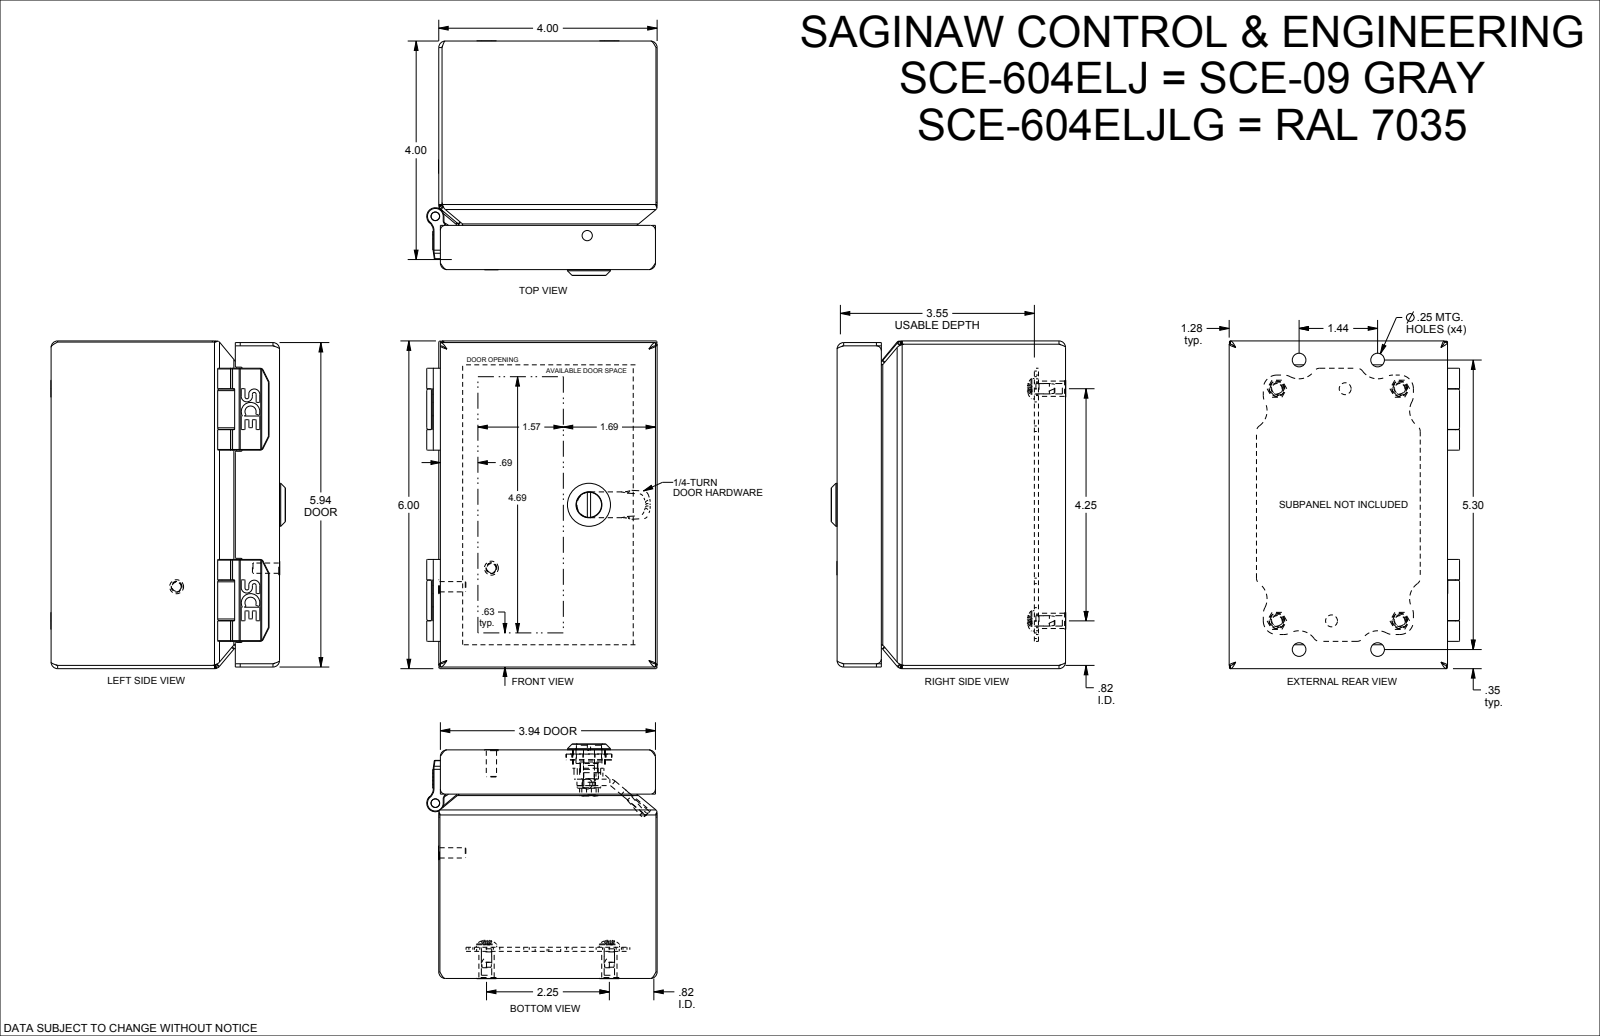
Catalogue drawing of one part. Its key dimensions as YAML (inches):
part_name: "SCE-604ELJLG"
step_written_by: "SolidWorks 2019 (CONFIG_CONTROL_DESIGN)"
units: inches
bodies: {solids: 0, faces: 2654, planar: 858, cylindrical: 764, other: 1032}
overall_size: [6, 4.296, 4.22]
round_holes:
  - {diameter: 0.25, count: 8}
  - {diameter: 0.19, count: 4}
  - {diameter: 0.284, count: 4}
  - {diameter: 0.479, count: 4}
  - {diameter: 0.02, count: 2}
  - {diameter: 0.1, count: 2}
  - {diameter: 0.174, count: 2}
  - {diameter: 0.196, count: 2}
  - {diameter: 0.218, count: 2}
  - {diameter: 0.266, count: 2}
  - {diameter: 0.158, count: 1}
  - {diameter: 0.187, count: 1}
round_bosses_or_shafts:
  - {diameter: 0.188, count: 6}
  - {diameter: 0.373, count: 4}
  - {diameter: 0.28, count: 4}
  - {diameter: 0.17, count: 4}
  - {diameter: 0.16, count: 4}
  - {diameter: 0.135, count: 4}
  - {diameter: 0.108, count: 4}
  - {diameter: 0.26, count: 2}
partial_cylinders:
  - {radius: 0.106, count: 132}
  - {radius: 0.005, count: 131}
  - {radius: 0.008, count: 32}
  - {radius: 0.01, count: 26}
  - {radius: 0.025, count: 24}
  - {radius: 0.03, count: 24}
  - {radius: 0.06, count: 22}
  - {radius: 0.013, count: 21}
face_to_face_distances: [0.06, 0.06, 3.94, 5.94, 4.124, 4.065, 4.185, 4.125, 4, 3.88]
hole_center_spacings: [3.5, 0.664, 1.917, 4.792, 5.119, 0.793, 0.994, 1]
